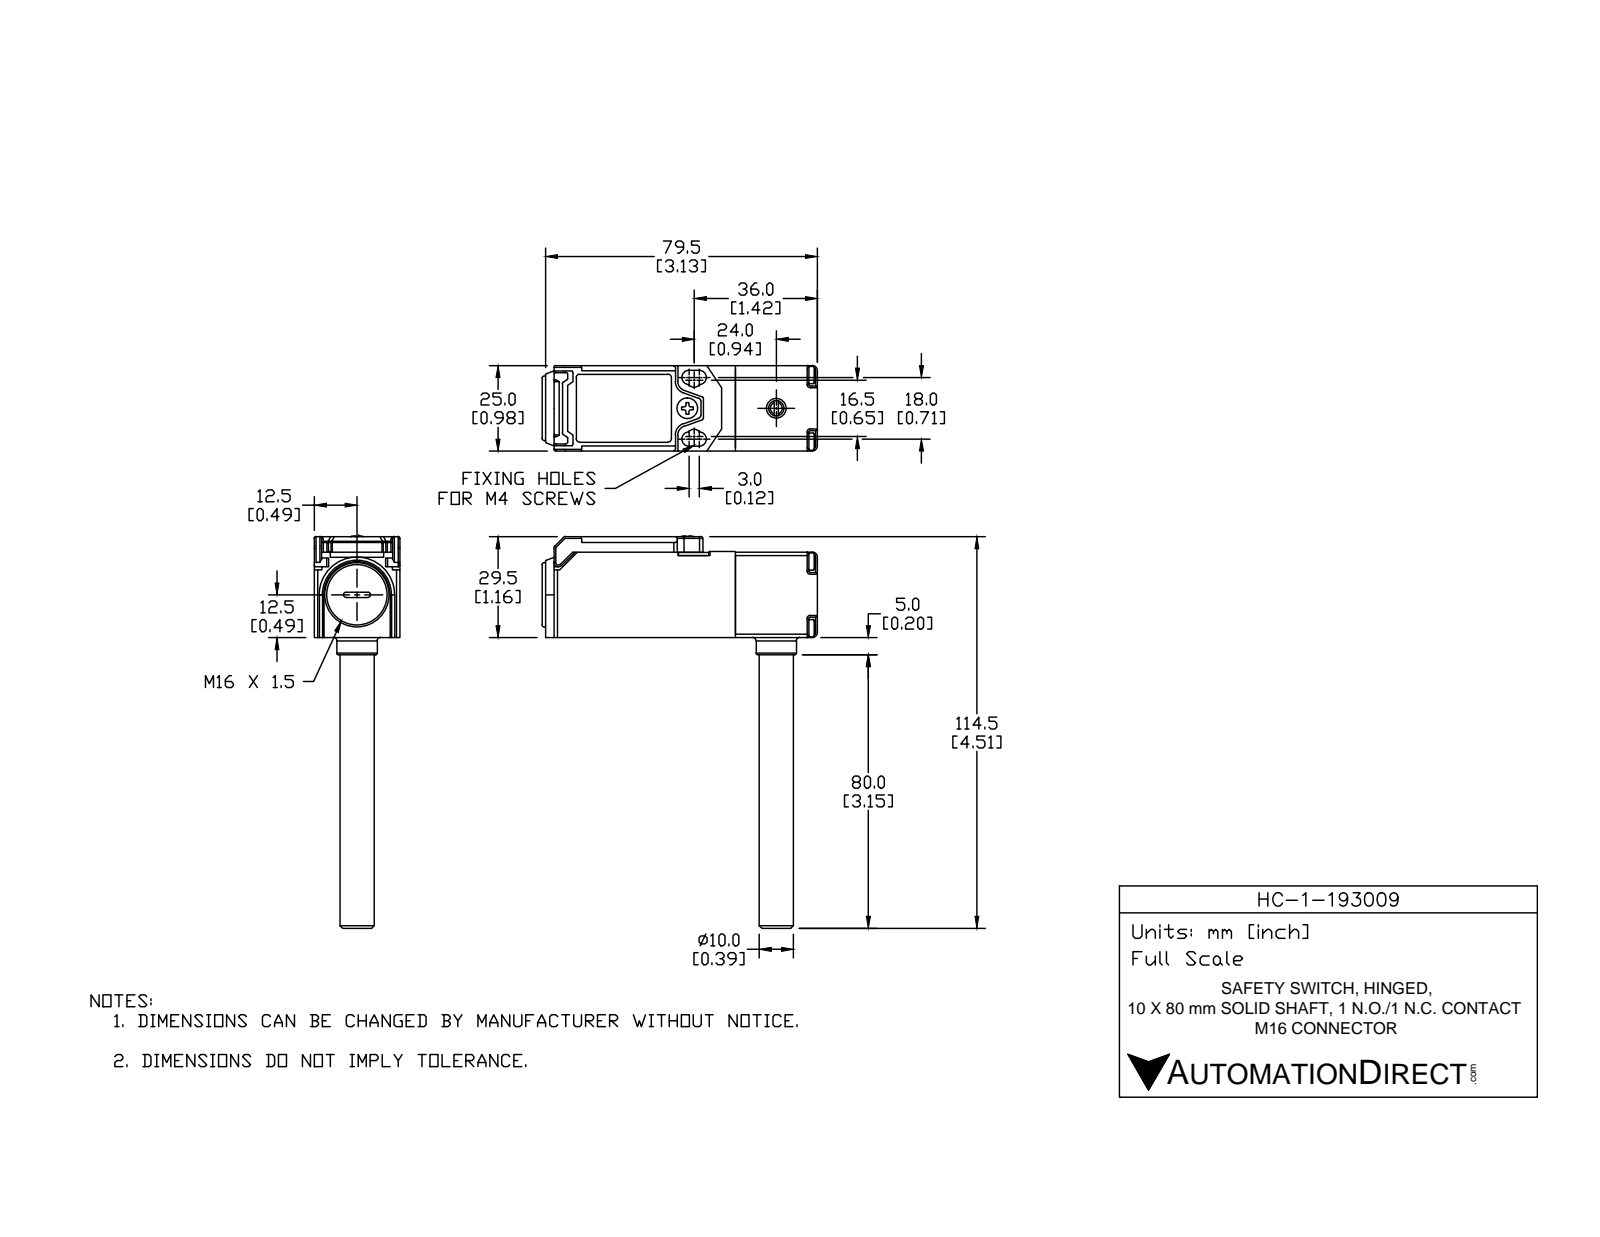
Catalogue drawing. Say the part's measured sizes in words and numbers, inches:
The part is named "HC-1-193009". Its 3-D file was written by "SolidWorks 2014 (AUTOMOTIVE_DESIGN)". It is 14 solids with 1702 faces: 700 planar, 601 cylindrical and 401 other. Overall it measures 4.517 by 3.169 by 0.984 inches. Its volume is 1.932 cubic inches and its surface area 44.5 square inches. Round holes: 5 of diameter 0.126, 4 of diameter 0.094, 2 of diameter 0.059, 2 of diameter 0.063, 2 of diameter 0.071, 2 of diameter 0.087, 2 of diameter 0.142, 1 of diameter 0.055, 1 of diameter 0.081, 1 of diameter 0.098, 1 of diameter 0.102, 1 of diameter 0.185. Round bosses or shafts: 5 of diameter 0.102, 4 of diameter 0.197, 4 of diameter 0.079, 2 of diameter 0.138, 1 of diameter 0.74, 1 of diameter 0.531, 1 of diameter 0.394, 1 of diameter 0.386. Partial cylindrical surfaces (rounded edges, fillets, slot ends): 226 of radius 0.02, 24 of radius 0.004, 20 of radius 0.012, 20 of radius 0.039, 7 of radius 0.059, 6 of radius 0.083, 6 of radius 0.11, 4 of radius 0.008. The main face-to-face distances are 0.984, 0.079, 0.071, 0.913, 0.039, 0.906, 0.945, 0.827, 0.874, 1.15. The hole center spacings are 0.543, 0.768, 0.171, 0.187, 0.245, 0.414, 0.423, 0.426.
